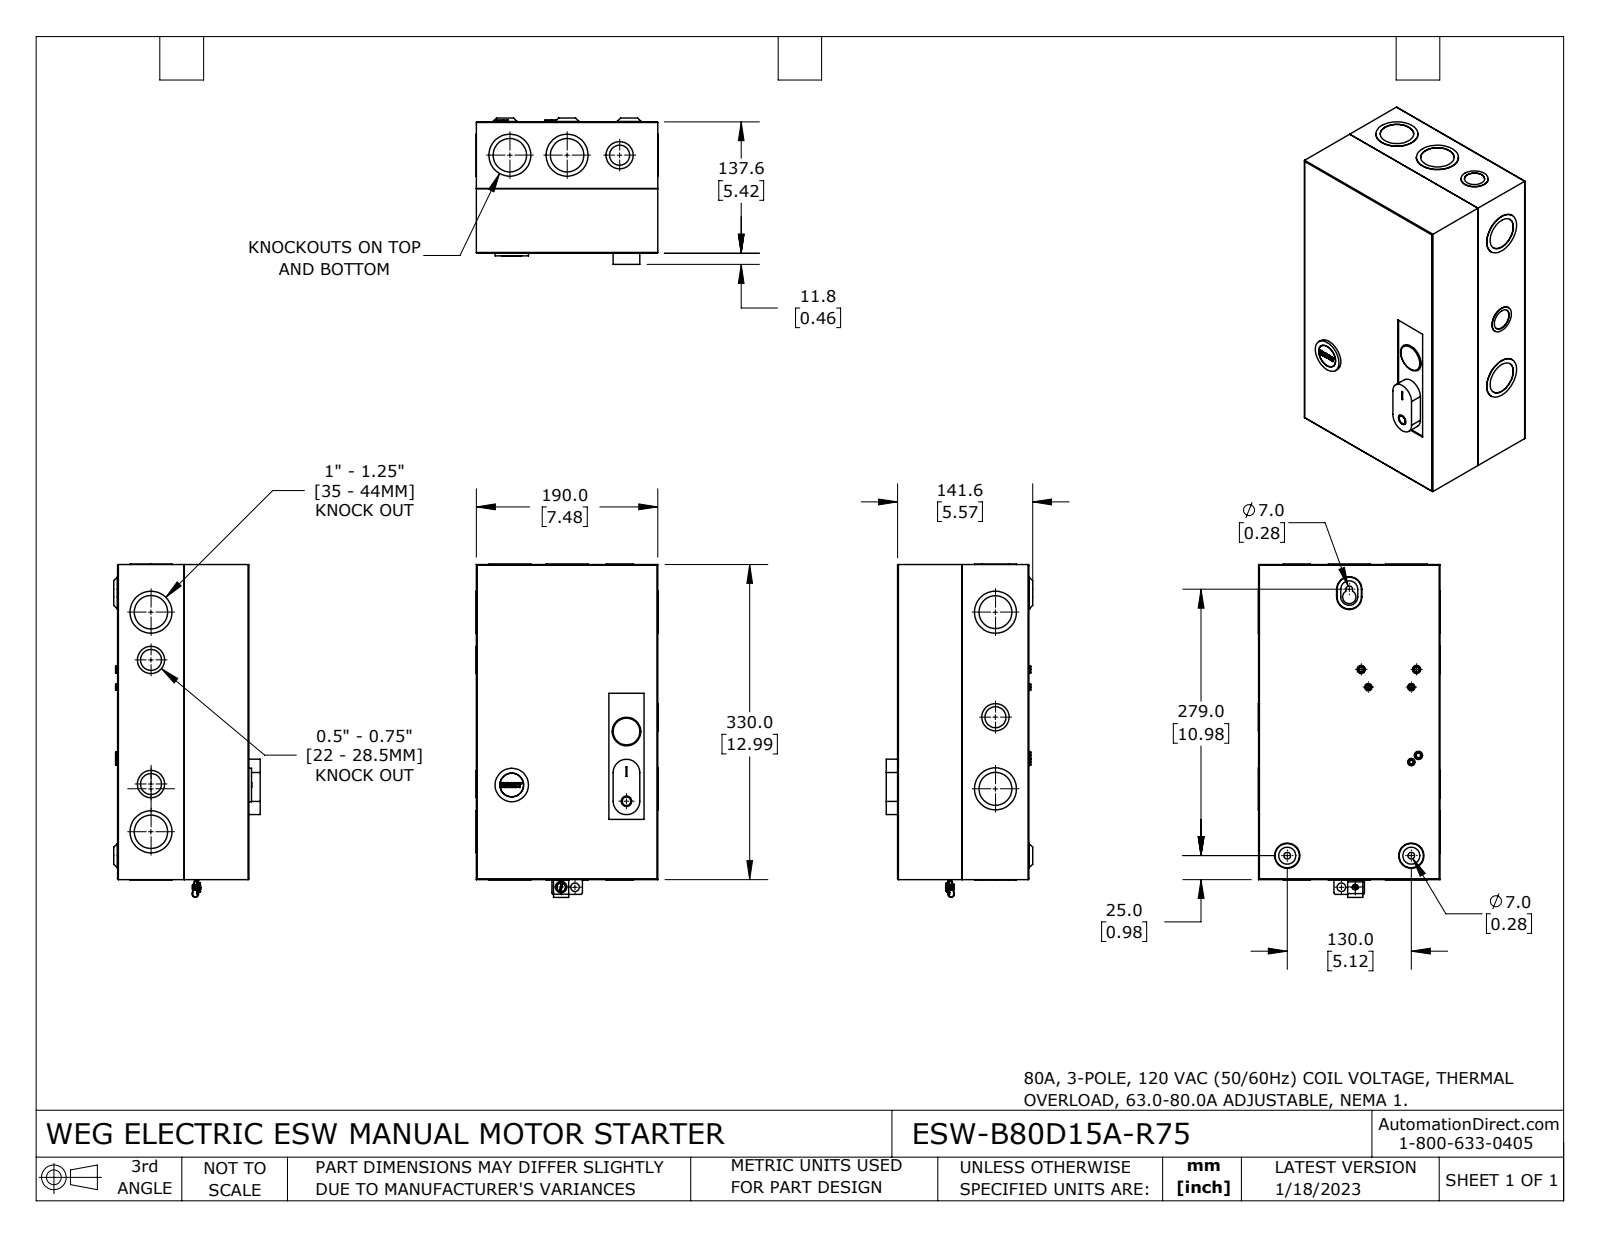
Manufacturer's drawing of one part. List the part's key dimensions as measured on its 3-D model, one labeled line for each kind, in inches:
Part name (STEP PRODUCT): ESW-B80D15A-R75
STEP written by: SolidWorks 2021 (CONFIG_CONTROL_DESIGN)
Units: inches
Bodies: 7 solids, 435 faces (161 planar, 221 cylindrical, 53 other)
Overall size (bounding box): 13.74 × 7.504 × 6.039
Volume: 24.58 in³ · Surface area: 936.7 in²
Round holes (diameter × count): ⌀1.378 ×4, ⌀0.146 ×3, ⌀0.183 ×3, ⌀0.276 ×2, ⌀0.866 ×2, ⌀0.886 ×2, ⌀1.357 ×2, ⌀0.256 ×1, ⌀0.279 ×1, ⌀0.354 ×1, ⌀0.433 ×1, ⌀0.469 ×1
Round bosses / shafts (diameter × count): ⌀1.732 ×4, ⌀1.122 ×3, ⌀0.278 ×3, ⌀0.24 ×3, ⌀1.734 ×2, ⌀1.378 ×1, ⌀1.193 ×1, ⌀1.148 ×1
Partial cylindrical surfaces — rounded edges, fillets, slot ends (radius × count): R0.004 ×34, R0.031 ×8, R0.079 ×3, R0.138 ×3, R0.059 ×2, R0.075 ×2, R0.108 ×2, R0.122 ×2
Main face-to-face distances: 0.047, 5.37, 7.433, 5.323, 5.417, 12.945, 7.386, 7.48, 0.071, 12.898
Hole centre spacings: 0.571, 1.772, 1.969, 2.283, 2.362, 5.118, 7.087, 10.972
